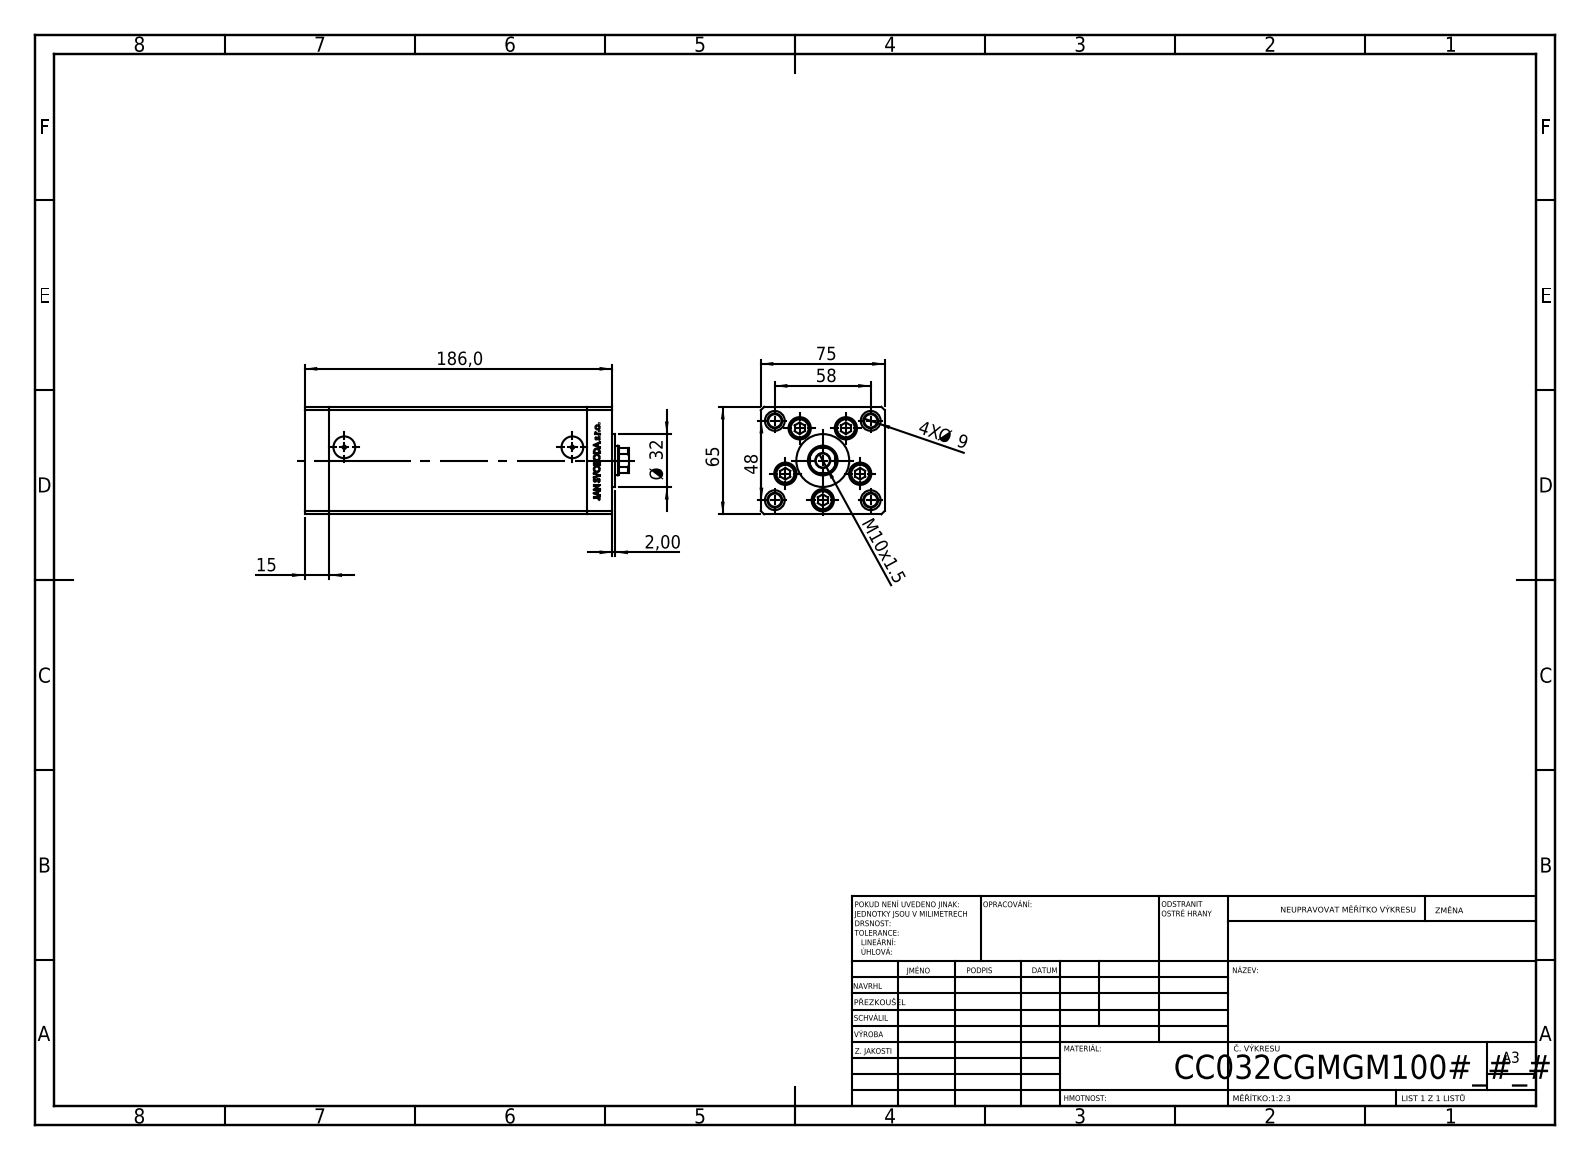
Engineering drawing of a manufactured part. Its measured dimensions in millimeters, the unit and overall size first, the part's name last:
Units: millimetres
Overall size (bounding box): 196 × 75 × 65
Round holes (diameter × count): ⌀9 ×9, ⌀13.5 ×5, ⌀8 ×4, ⌀12 ×4, ⌀2 ×2, ⌀13.16 ×2, ⌀8.5 ×1, ⌀12.5 ×1, ⌀18 ×1
Round bosses / shafts (diameter × count): ⌀8 ×5, ⌀12.5 ×4, ⌀32 ×1
Partial cylindrical surfaces — rounded edges, fillets, slot ends (radius × count): R0.93 ×2, R8.5 ×1
Main face-to-face distances: 75, 65, 15, 156, 171, 186, 28, 54.5, 10.5, 26.25
Hole centre spacings: 24, 37.64, 15.67, 17.22, 27.71, 28.83, 29, 32.63
Volume: 757 889 mm³ · Surface area: 153 912 mm²
Bodies: 13 solids, 1169 faces (540 planar, 167 cylindrical, 462 other)
Part name (STEP PRODUCT): ALLEN BOLT; V220C FRONT; V220C_C MIDDLE; V220C_VC_C (+1 more)
STEP written by: SolidWorks 2019 (CONFIG_CONTROL_DESIGN)
